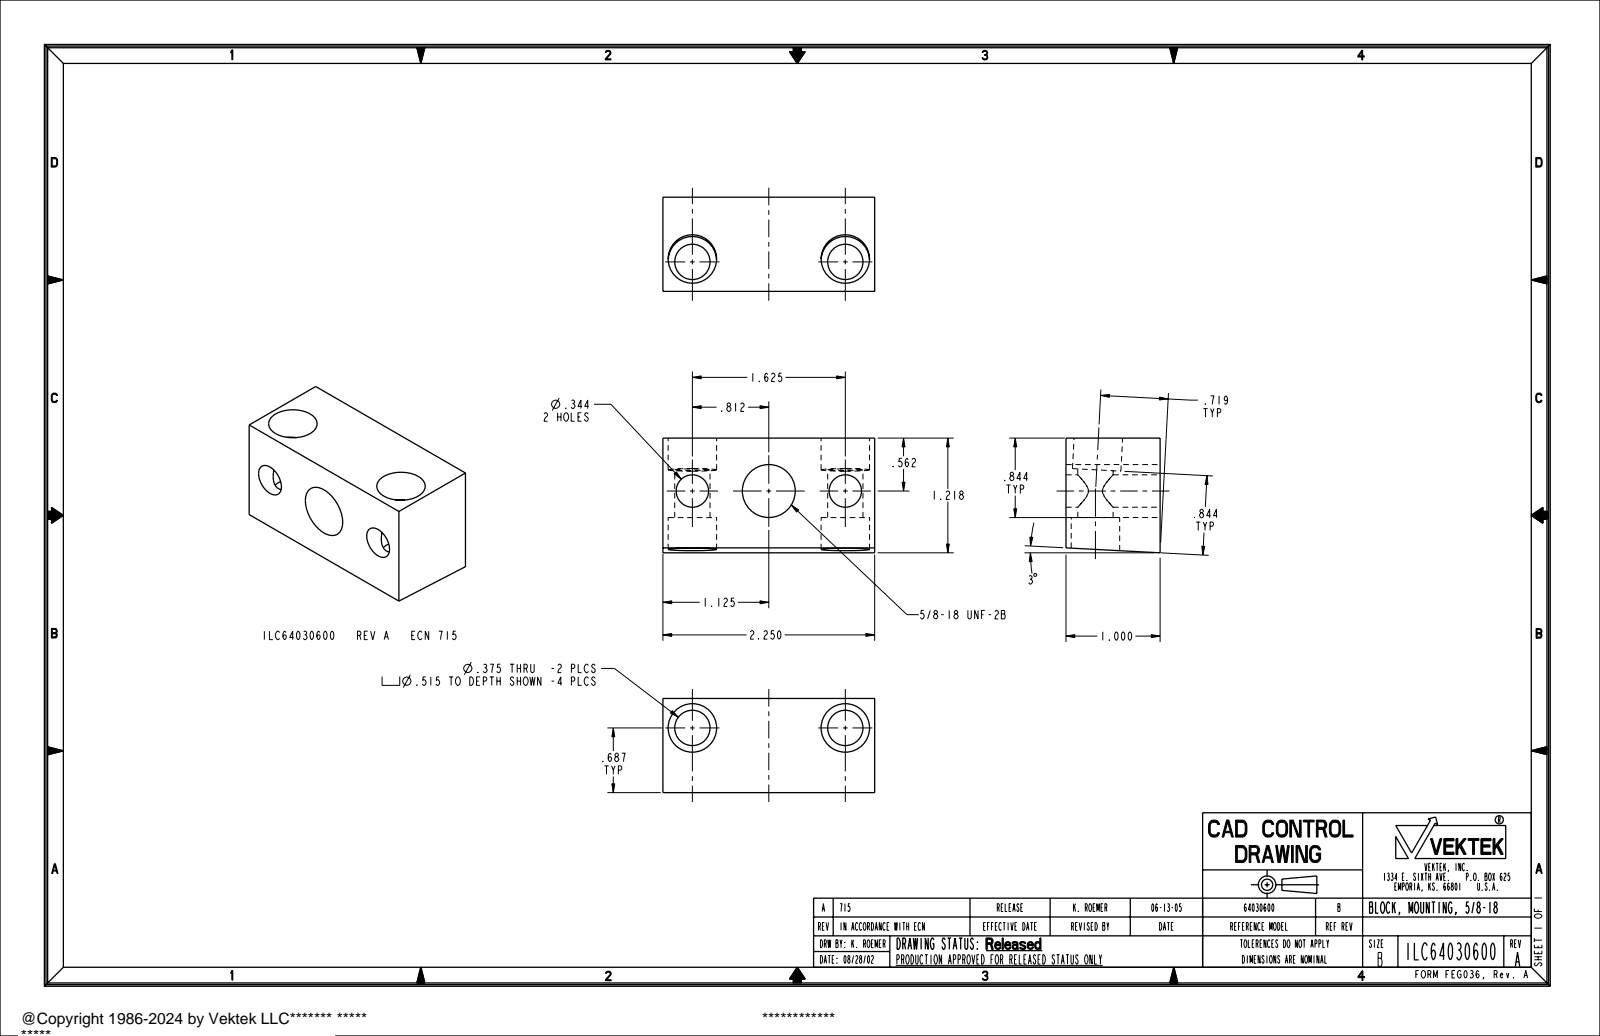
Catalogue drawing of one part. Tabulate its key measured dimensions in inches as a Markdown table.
| quantity | value |
| --- | --- |
| part name | ILC64030600 |
| STEP written by | PRO/ENGINEER BY PARAMETRIC TECHNOLOGY CORPORATION, 2004290 (AUTOMOTIVE_DESIGN_CC2) |
| units | inches |
| bodies | 1 solid, 32 faces (10 planar, 22 cylindrical, 0 other) |
| overall size | 2.25 × 1.218 × 1 |
| volume | 1.915 in³ |
| surface area | 17.22 in² |
| round holes (diameter × count) | 0.515 × 4, 0.344 × 2, 0.375 × 2, 0.562 × 1 |
| main face-to-face distances | 1, 2.25, 0.844, 0.845 |
| hole center spacings | 1.625, 0.812, 0.813 |
